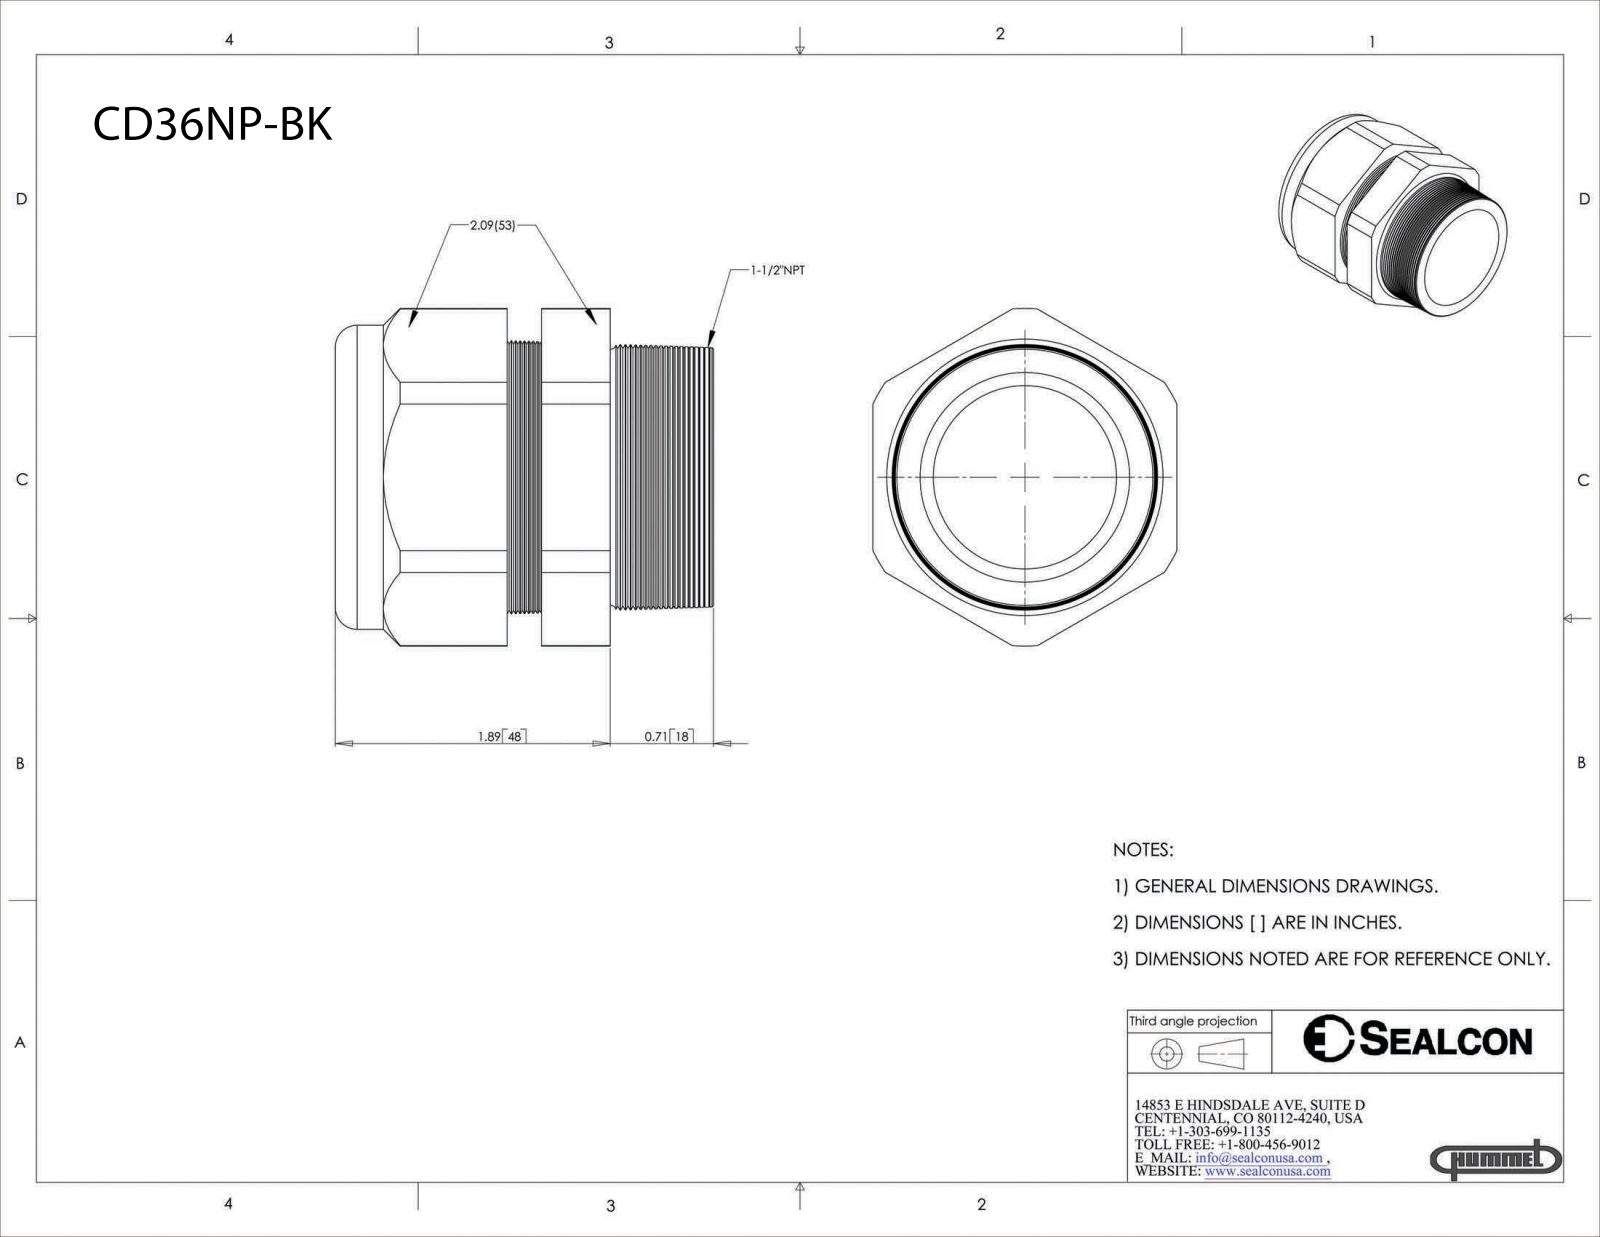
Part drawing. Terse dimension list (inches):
name: CD36NP-BK
written by: SolidWorks 2007 (CONFIG_CONTROL_DESIGN)
unit: in
bodies: 2 solids, 223 faces (21 planar, 20 cylindrical, 182 other)
size: 2.6 × 2.32 × 2.09
volume: 5.572 in³; area: 41.78 in²
holes: 1× ⌀1.24, 1× ⌀1.26
bosses: 1× ⌀2.09
rounds: 1× R1.16
face distances: 2.09, 0.5, 0.02, 0.48, 1.418, 1.398, 0.918, 1.181, 1.161, 0.681
